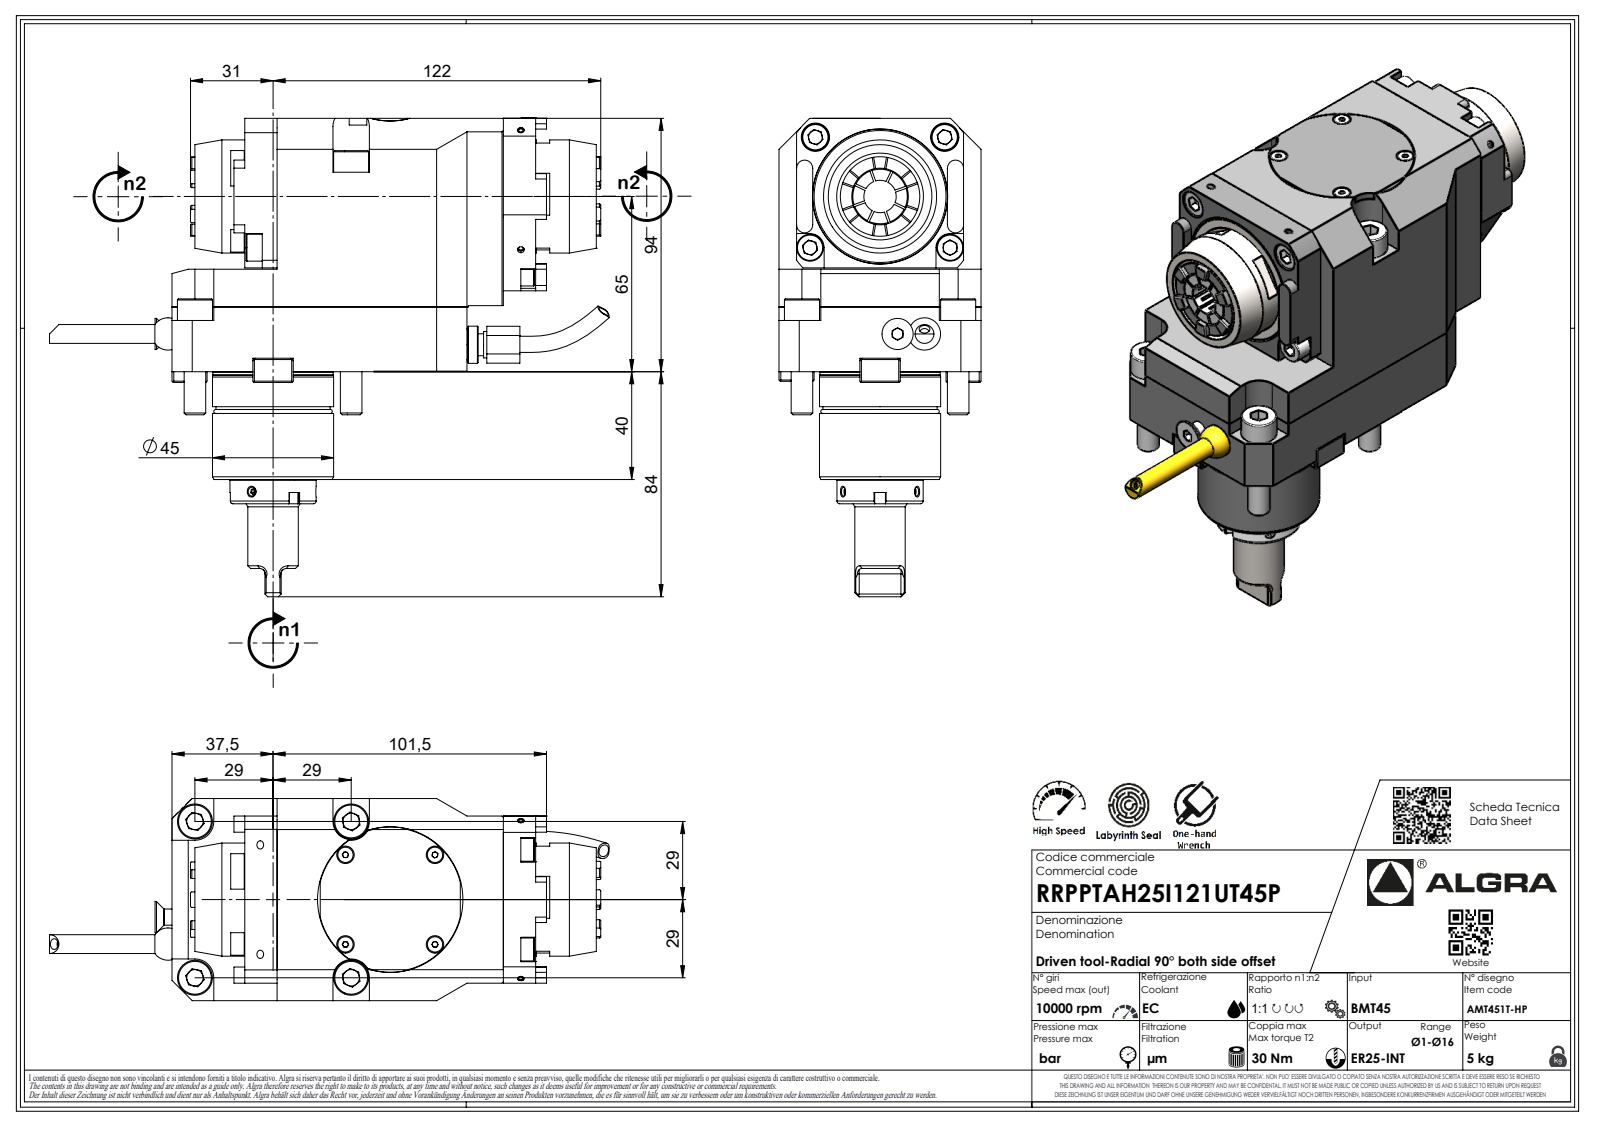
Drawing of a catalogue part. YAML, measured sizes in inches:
part_name: "RRPPTAH25I121UT45P"
step_written_by: "SolidWorks 2023 (AUTOMOTIVE_DESIGN)"
units: inches
bodies: {solids: 1, faces: 695, planar: 486, cylindrical: 105, other: 104}
overall_size: [8.181, 6.988, 2.953]
volume: 52.87
surface_area: 117.2
round_holes:
  - {diameter: 0.083, count: 1}
  - {diameter: 0.157, count: 1}
round_bosses_or_shafts:
  - {diameter: 0.512, count: 4}
  - {diameter: 0.315, count: 4}
  - {diameter: 1.772, count: 1}
  - {diameter: 1.756, count: 1}
  - {diameter: 1.669, count: 1}
  - {diameter: 1.654, count: 1}
  - {diameter: 1.26, count: 1}
  - {diameter: 0.736, count: 1}
partial_cylinders:
  - {radius: 0.079, count: 22}
  - {radius: 0.013, count: 7}
  - {radius: 0.02, count: 7}
  - {radius: 0.146, count: 7}
  - {radius: 0.118, count: 4}
  - {radius: 0.374, count: 3}
  - {radius: 0.266, count: 2}
  - {radius: 0.276, count: 2}
face_to_face_distances: [2.953, 0.256, 2.697, 3.701, 3.693, 2.205, 1.496, 1.488, 2.441, 0.531]
